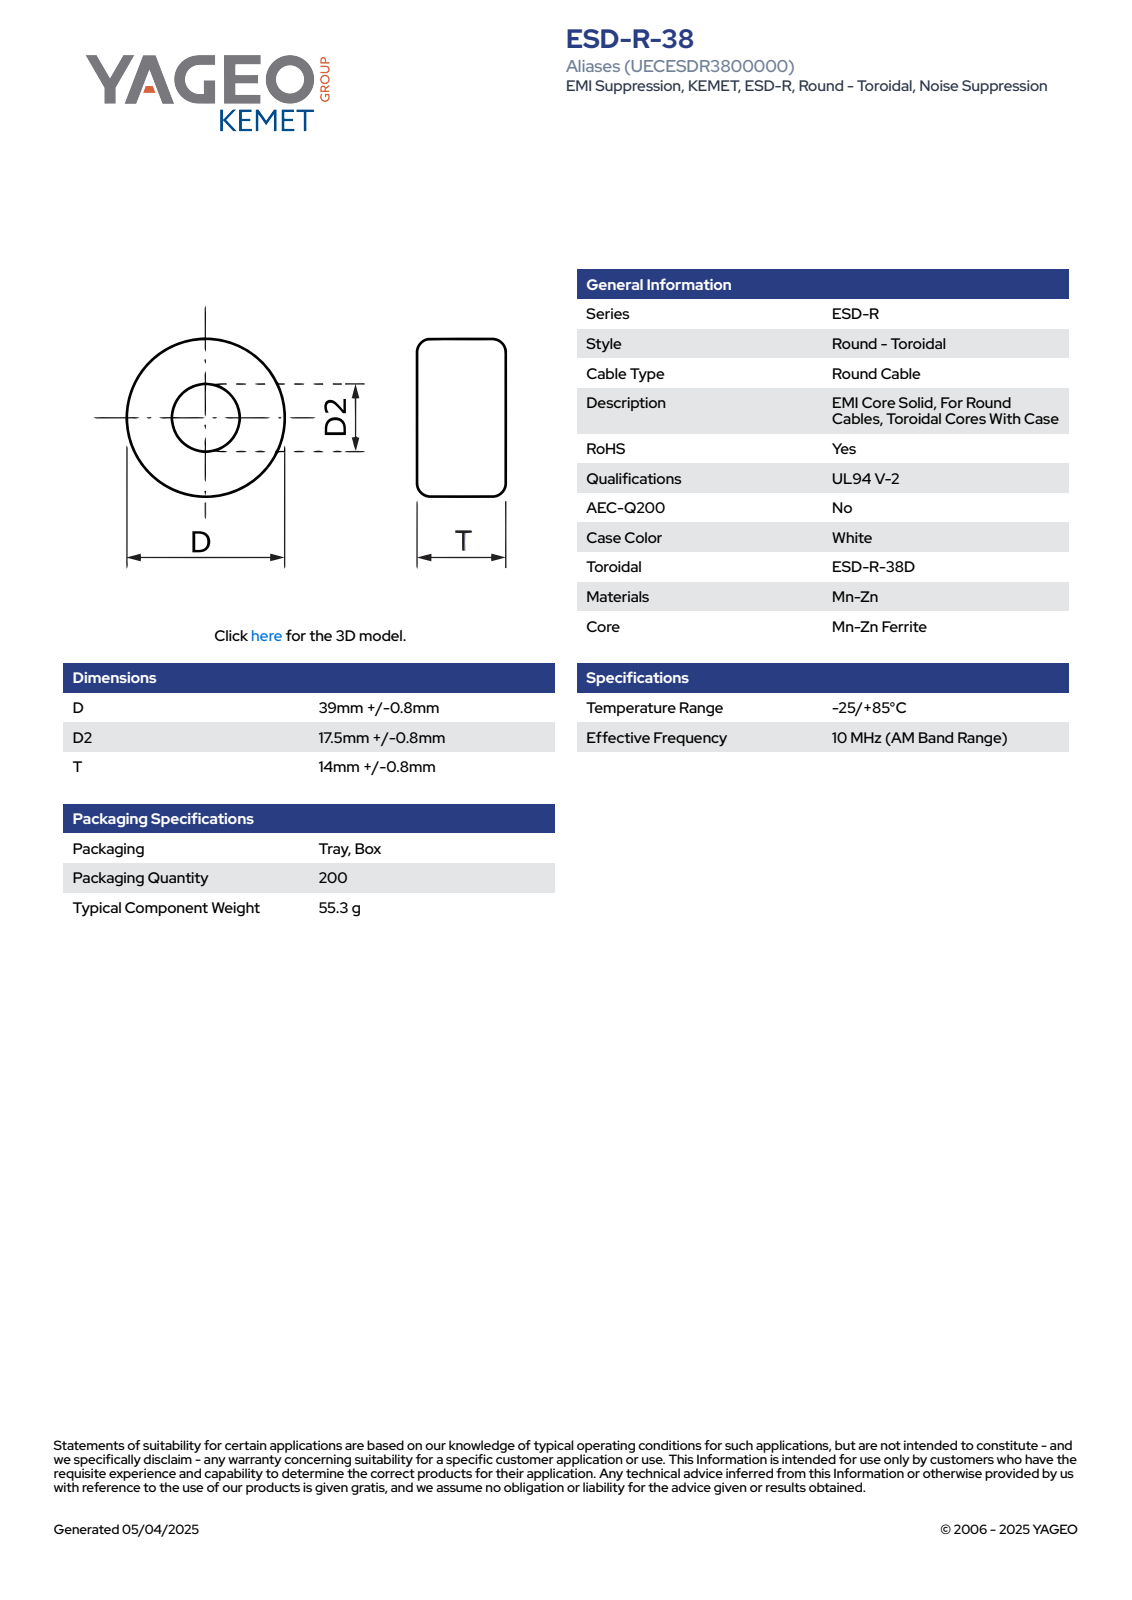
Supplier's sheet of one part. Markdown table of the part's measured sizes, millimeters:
| quantity | value |
| --- | --- |
| part name | EC_KBC_D39.8D217.5T14.8 |
| STEP written by | SolidWorks 2021 (AUTOMOTIVE_DESIGN) |
| units | millimeters |
| bodies | 1 solid, 66 faces (24 planar, 7 cylindrical, 35 other) |
| overall size | 39.81 × 39.8 × 14.8 |
| volume | 14 770 mm³ |
| surface area | 4 550 mm² |
| round holes (diameter × count) | 17.5 × 1 |
| round bosses / shafts (diameter × count) | 39.8 × 1 |
| partial cylindrical surfaces (radius × count) | 19.91 × 1 |
| main face-to-face distances | 14.8, 6.55, 8.25, 1.7, 0.32, 6.87, 7.93, 1.38, 1.06, 7.61 |
